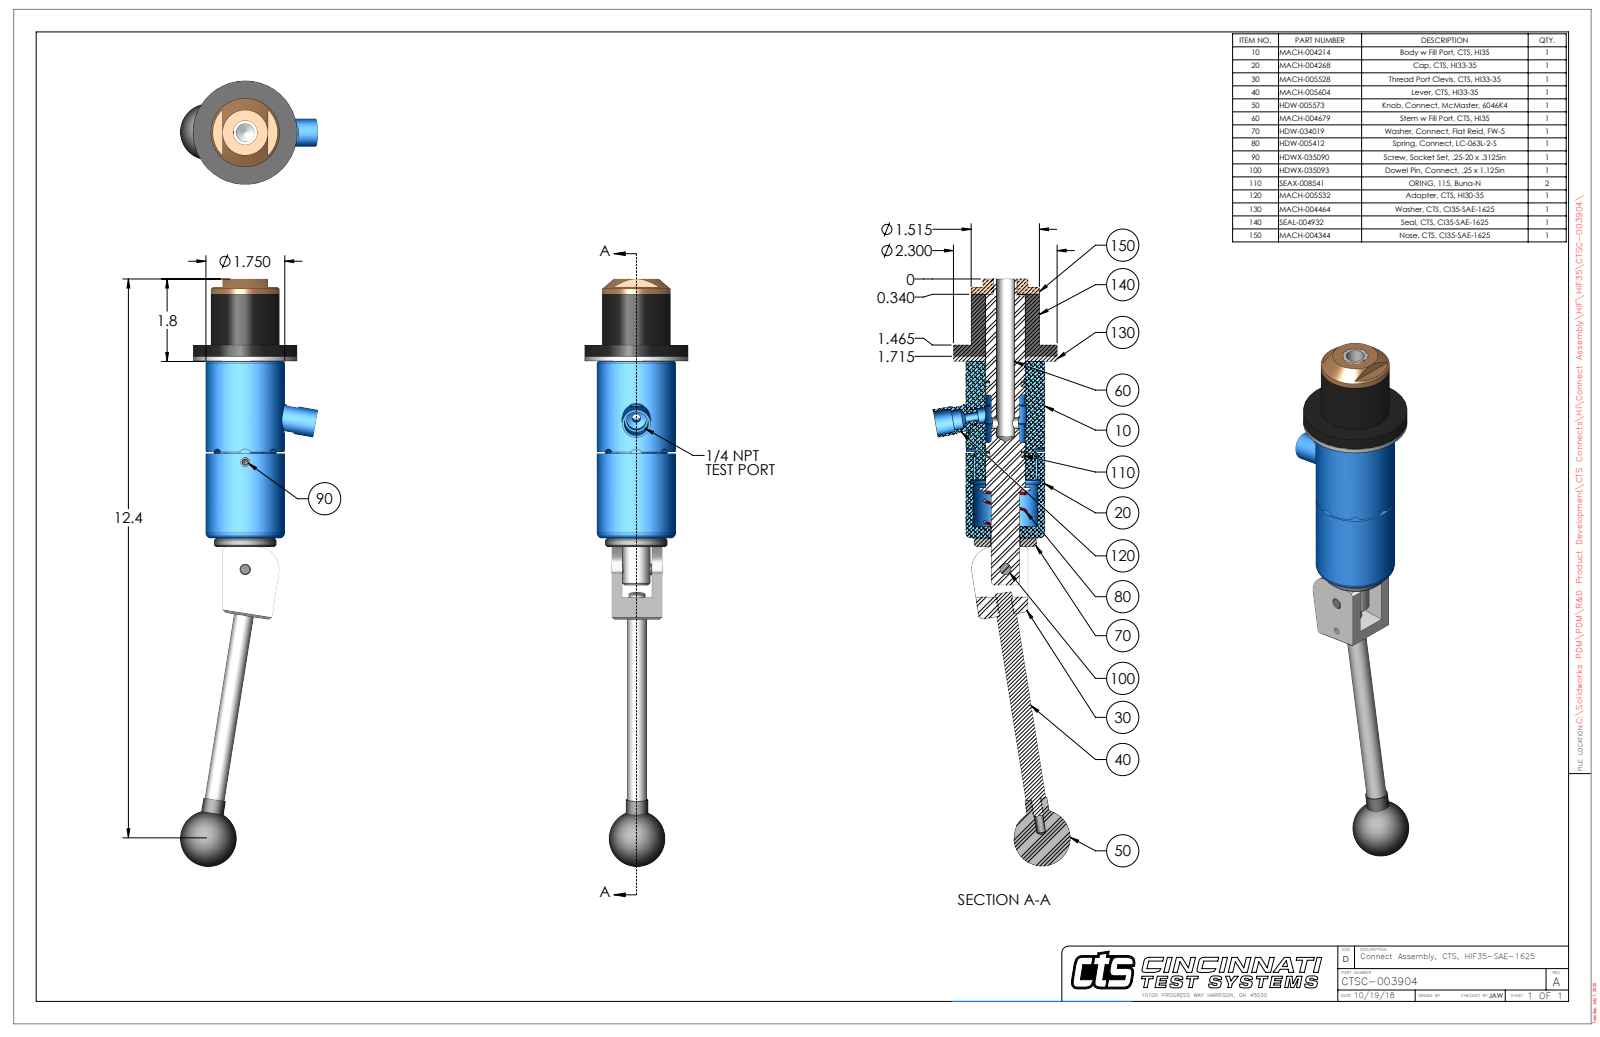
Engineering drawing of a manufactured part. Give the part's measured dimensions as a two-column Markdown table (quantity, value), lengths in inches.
| quantity | value |
| --- | --- |
| part name | CTSC-003904 |
| STEP written by | SolidWorks 2023 (AUTOMOTIVE_DESIGN) |
| units | inches |
| bodies | 9 solids, 282 faces (104 planar, 117 cylindrical, 61 other) |
| overall size | 13.02 × 3.043 × 2.3 |
| volume | 16.32 in³ |
| surface area | 101.9 in² |
| round holes (diameter × count) | 0.201 × 2, 0.15 × 1, 0.187 × 1, 0.249 × 1, 0.25 × 1, 0.251 × 1, 0.313 × 1, 0.406 × 1, 0.438 × 1, 0.531 × 1, 0.635 × 1, 0.656 × 1 |
| round bosses / shafts (diameter × count) | 0.25 × 2, 2.3 × 1, 1.75 × 1, 1.515 × 1, 1.515 × 1, 1.38 × 1, 0.869 × 1, 0.625 × 1 |
| partial cylindrical surfaces (radius × count) | 0.125 × 4, 0.029 × 2, 0.242 × 1, 0.33 × 1, 0.5 × 1, 0.695 × 1, 0.819 × 1 |
| main face-to-face distances | 0.11, 1.375, 1.485, 5.405, 4.03, 3.92, 0.25, 1.125, 0.36, 4.28 |
| hole center spacings | 0.74, 2.376, 3.116 |
